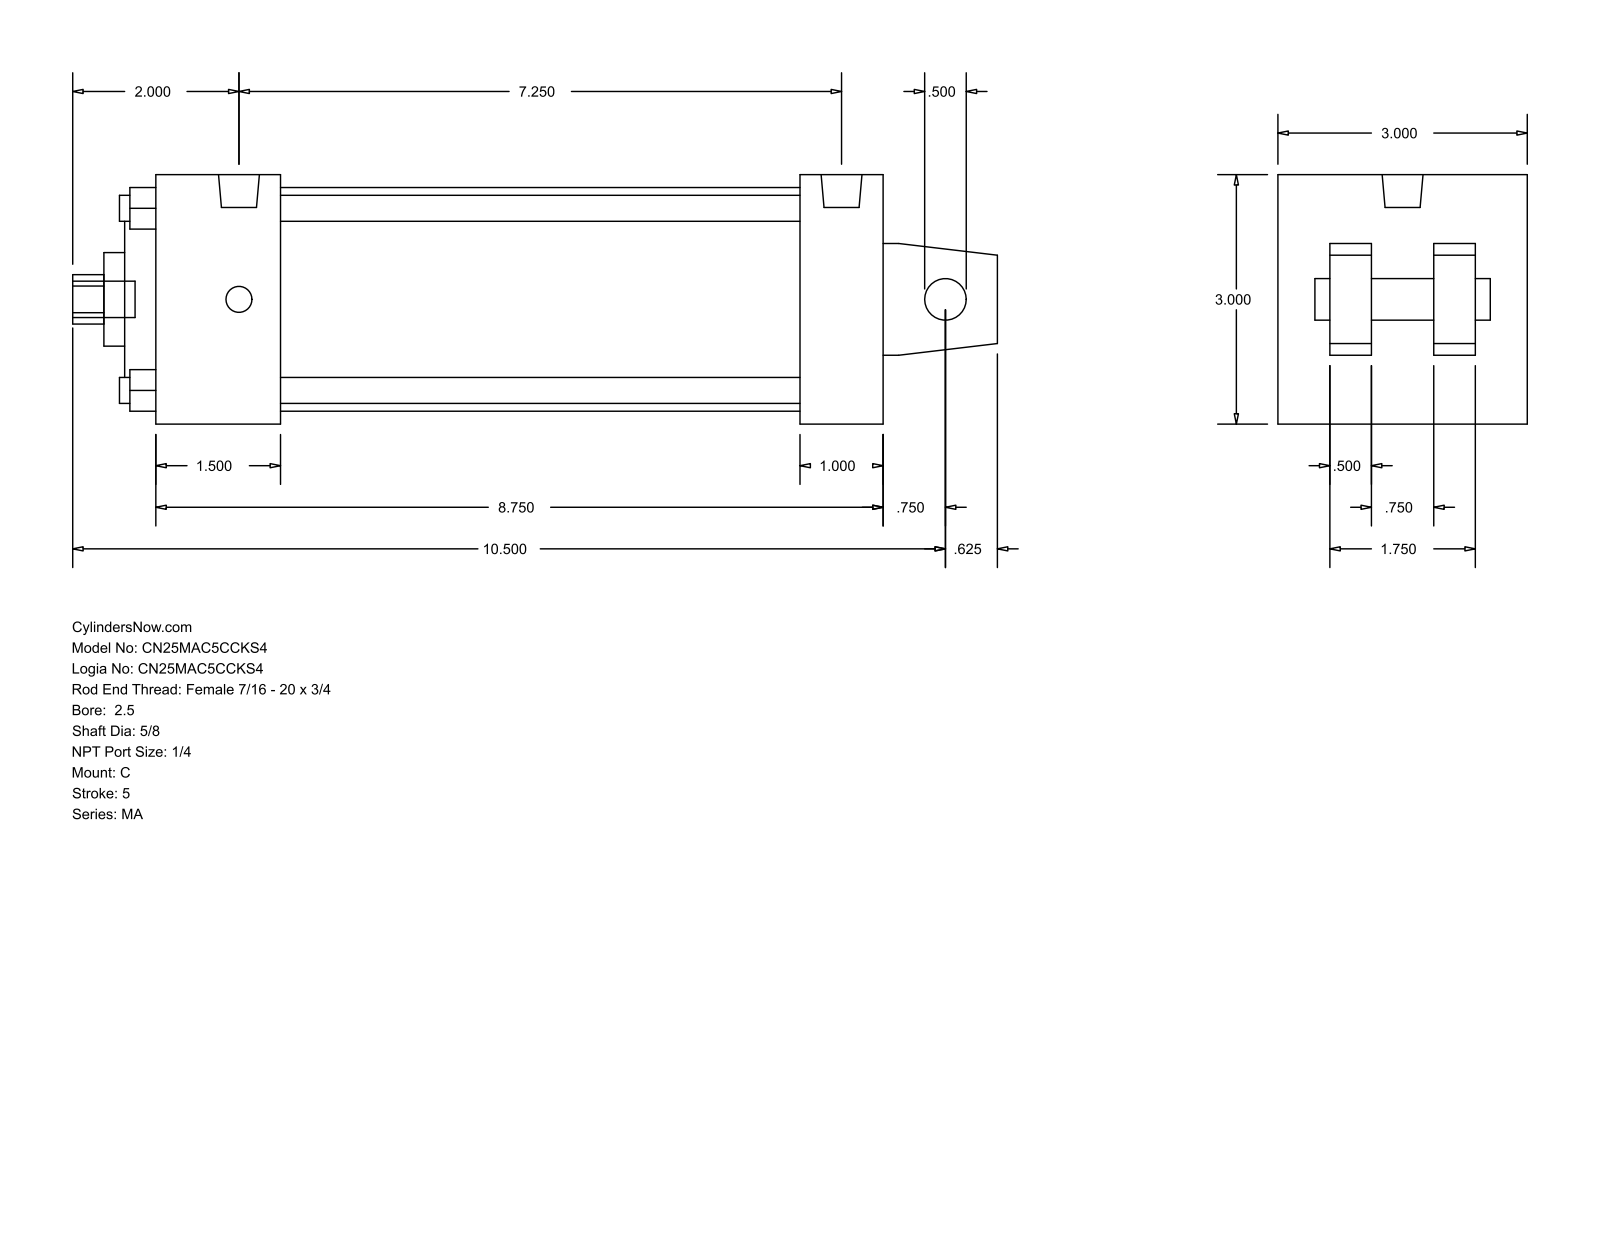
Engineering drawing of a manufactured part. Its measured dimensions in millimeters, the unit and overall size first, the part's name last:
Units: millimetres
Overall size (bounding box): 282.57 × 76.2 × 76.2
Round holes (diameter × count): ⌀7.94 ×4, ⌀12.7 ×1, ⌀15.88 ×1, ⌀28.57 ×1, ⌀50.8 ×1, ⌀68.33 ×1
Round bosses / shafts (diameter × count): ⌀7.94 ×4, ⌀12.49 ×2, ⌀11.11 ×1
Partial cylindrical surfaces — rounded edges, fillets, slot ends (radius × count): R7.54 ×1
Main face-to-face distances: 76.2, 222.25, 12.7, 15.87, 47.63, 25.4, 38.1, 196.85, 158.75, 184.15
Hole centre spacings: 39.33, 55.62, 78.66
Bodies: 0 solids, 105 faces (77 planar, 28 cylindrical, 0 other)
Part name (STEP PRODUCT): MA_C__0250_0.625
STEP written by: GSSL Pune (CONFIG_CONTROL_DESIGN)
